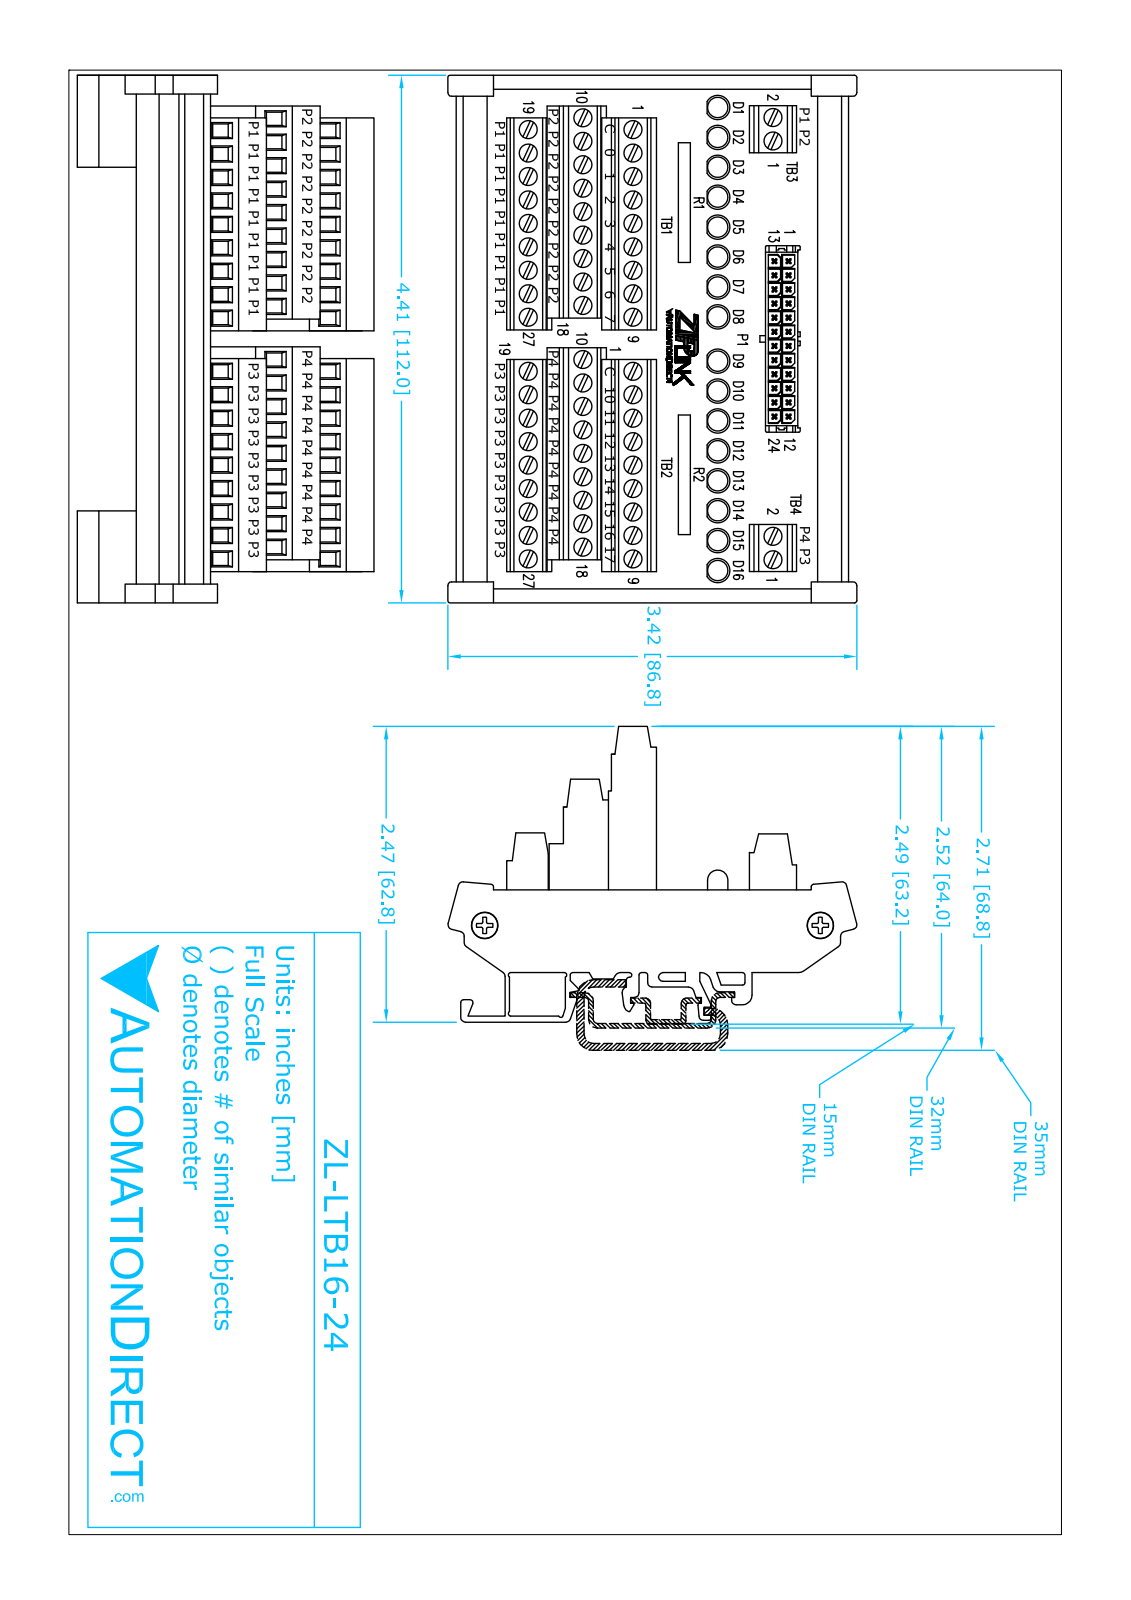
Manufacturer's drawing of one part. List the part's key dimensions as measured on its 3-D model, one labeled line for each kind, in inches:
Part name (STEP PRODUCT): ZL-LTB16-24
STEP written by: SolidWorks 2014 (AUTOMOTIVE_DESIGN)
Units: inches
Bodies: 1 solid, 1650 faces (1333 planar, 241 cylindrical, 76 other)
Overall size (bounding box): 4.466 × 3.42 × 2.48
Volume: 13.31 in³ · Surface area: 81.66 in²
Round holes (diameter × count): ⌀0.15 ×58, ⌀0.225 ×2
Round bosses / shafts (diameter × count): ⌀0.205 ×2
Partial cylindrical surfaces — rounded edges, fillets, slot ends (radius × count): R0.015 ×41, R0.03 ×15
Main face-to-face distances: 0.628, 0.1, 4.41, 0.03, 0.658, 0.16, 0.26, 2.03, 1.08, 0.452
Hole centre spacings: 0.196, 0.828, 0.392, 0.895, 1.123, 0.383, 0.446, 0.588
